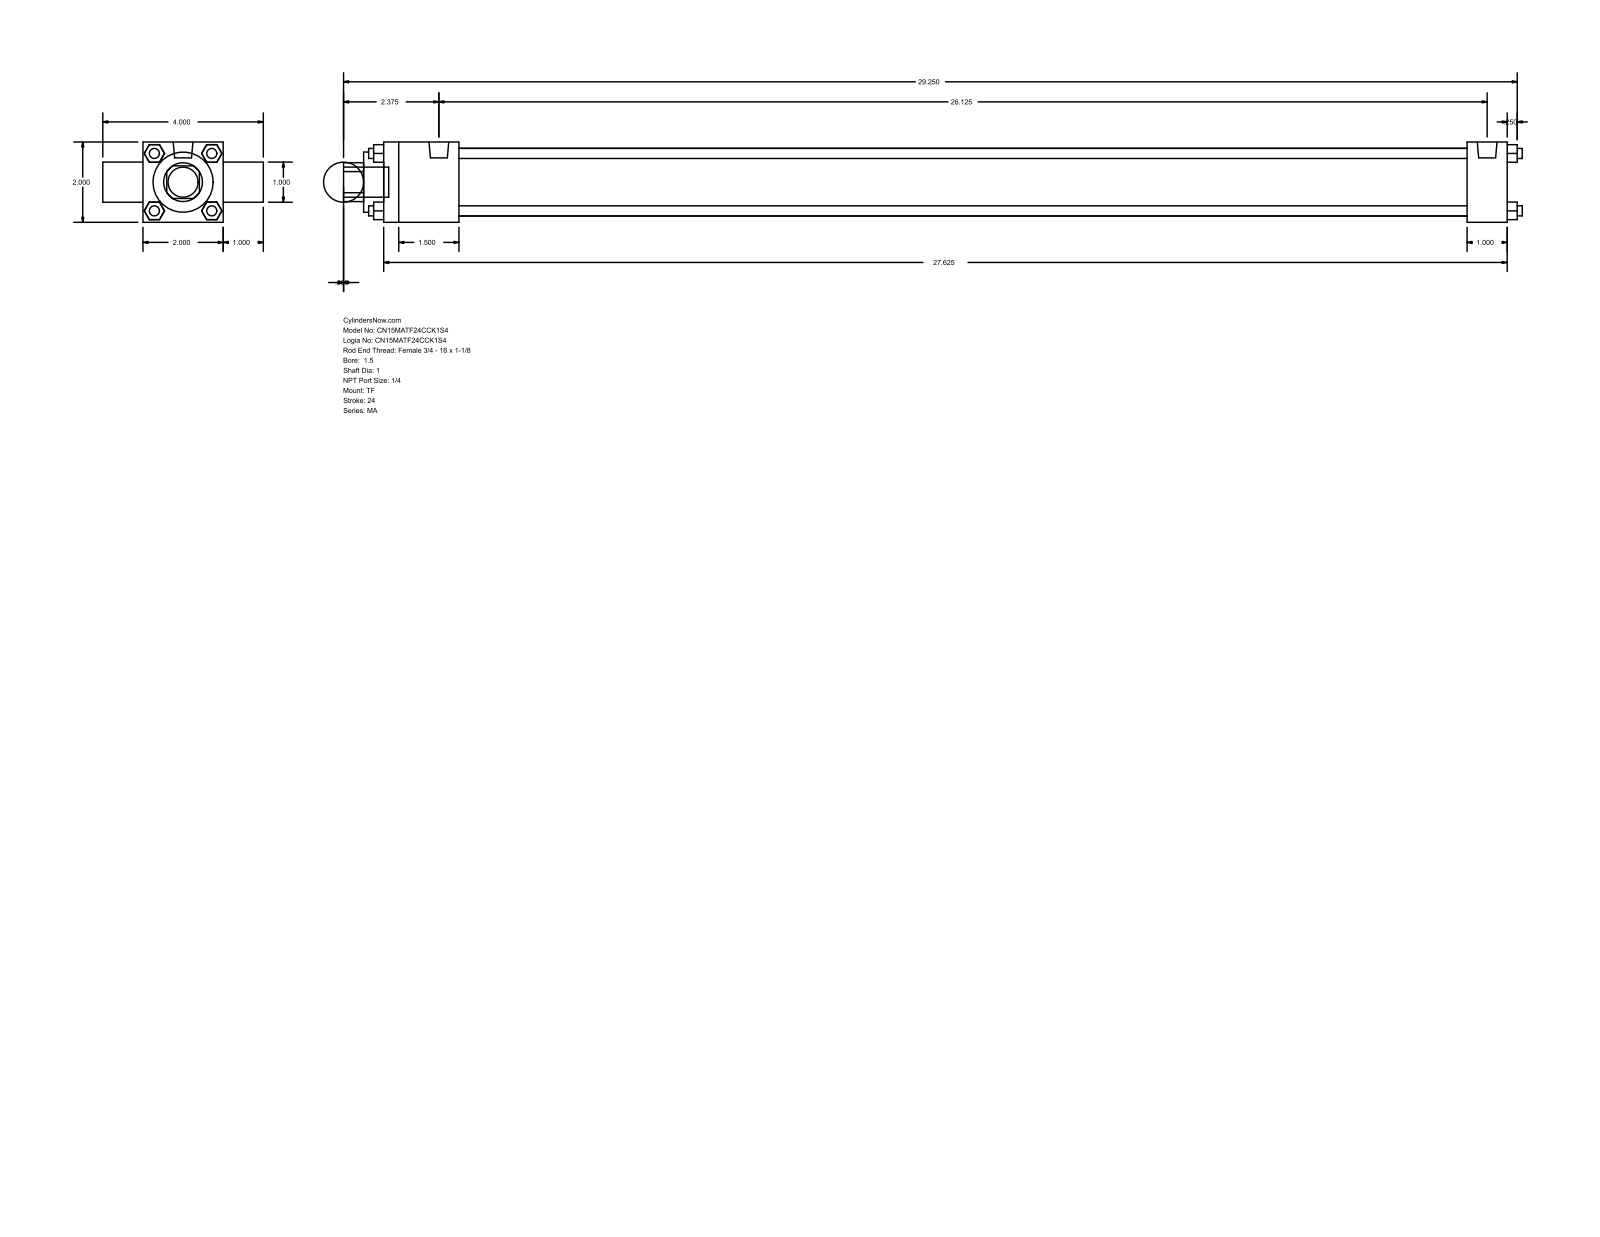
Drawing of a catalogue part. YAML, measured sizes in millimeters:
part_name: "MA_TF__0150_1"
step_written_by: "GSSL Pune (CONFIG_CONTROL_DESIGN)"
units: millimeters
bodies: {solids: 0, faces: 120, planar: 92, cylindrical: 28, other: 0}
overall_size: [746.12, 101.6, 50.8]
round_holes:
  - {diameter: 25.4, count: 2}
  - {diameter: 38.1, count: 1}
  - {diameter: 42.93, count: 1}
round_bosses_or_shafts:
  - {diameter: 6.35, count: 4}
  - {diameter: 7.94, count: 3}
  - {diameter: 12.49, count: 2}
  - {diameter: 19.05, count: 1}
partial_cylinders:
  - {radius: 12.29, count: 1}
face_to_face_distances: [50.8, 25.4, 711.2, 76.2, 6.35, 47.63, 685.8, 638.17, 663.57, 723.9]
